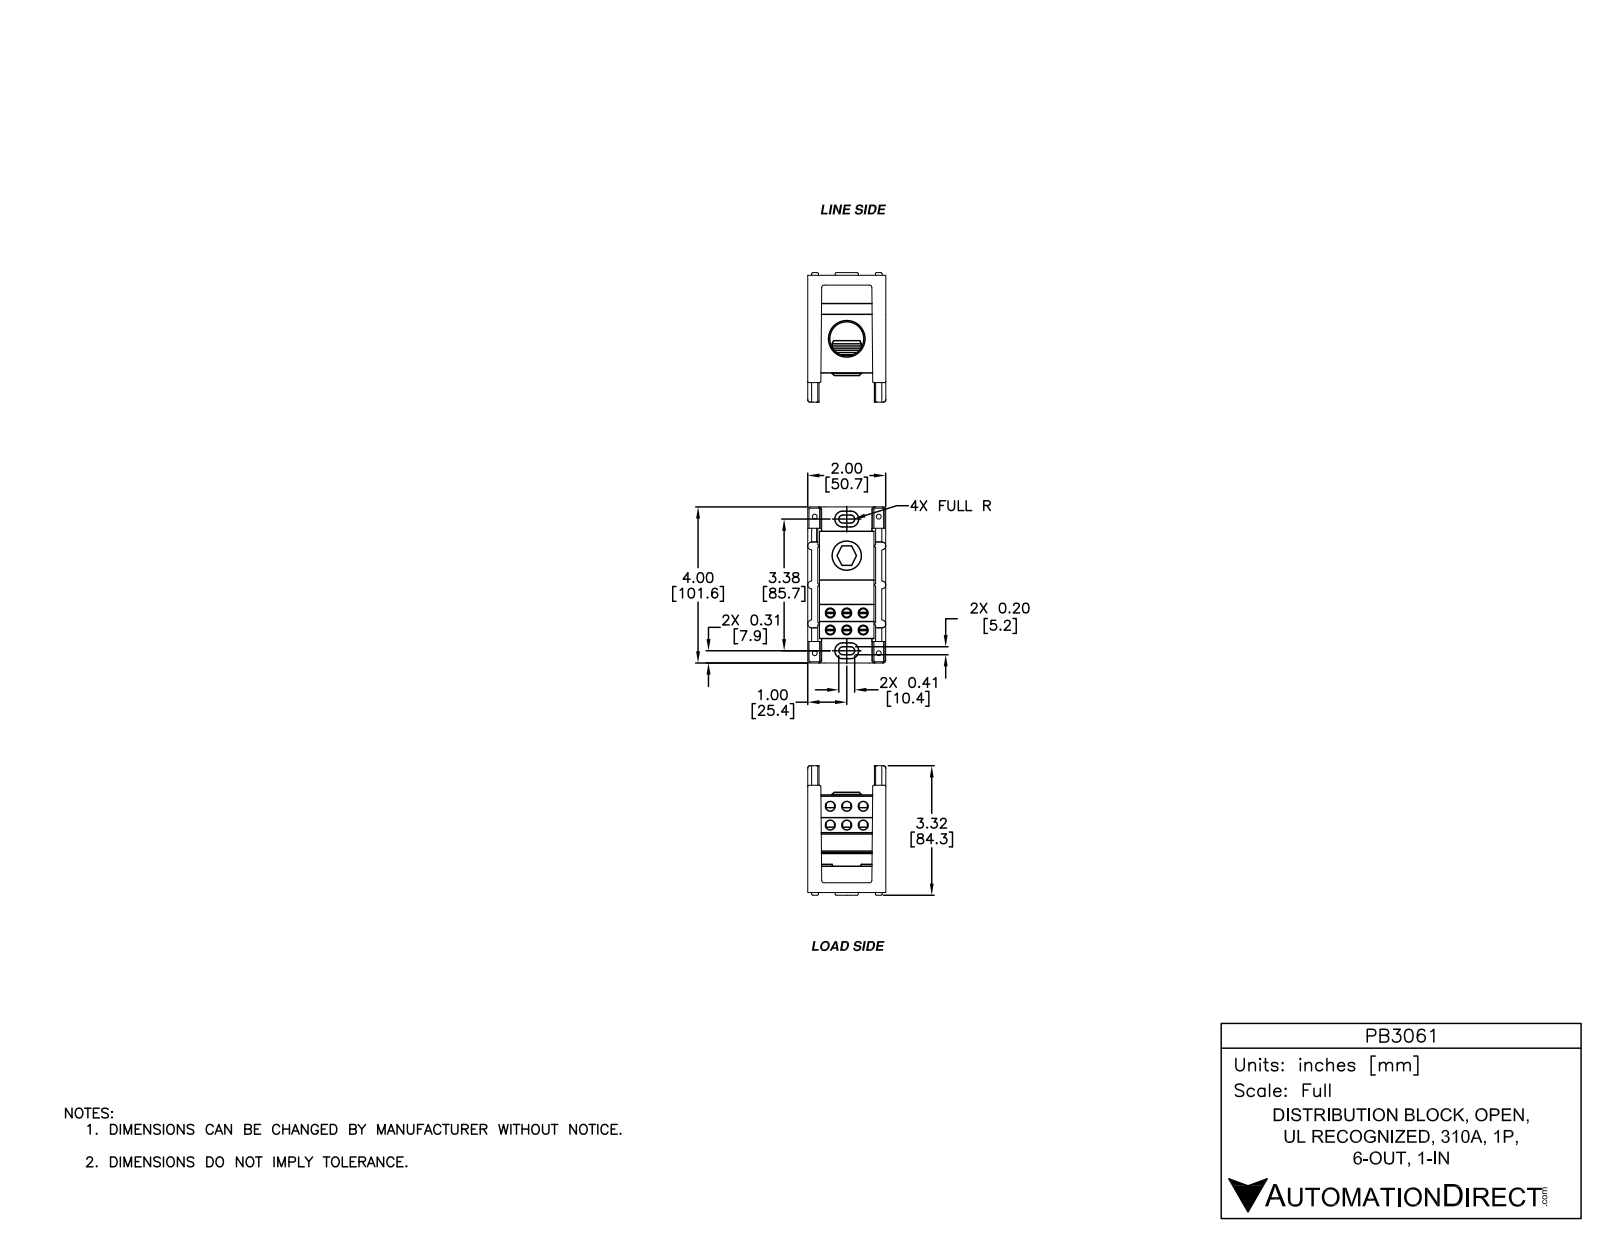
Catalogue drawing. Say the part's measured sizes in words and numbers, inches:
The part is named "PB3061". Its 3-D file was written by "SolidWorks 2014 (AUTOMOTIVE_DESIGN)". It is 5 solids with 562 faces: 220 planar, 234 cylindrical and 108 other. Overall it measures 4 by 3.35 by 2 inches. Its volume is 11.09 cubic inches and its surface area 117.4 square inches. Round holes: 6 of diameter 0.219, 6 of diameter 0.25, 4 of diameter 0.125, 2 of diameter 0.75, 1 of diameter 0.5, 1 of diameter 0.875. Round bosses or shafts: 4 of diameter 0.174, 2 of diameter 0.062, 1 of diameter 0.375. Partial cylindrical surfaces (rounded edges, fillets, slot ends): 50 of radius 0.031, 22 of radius 0.1, 18 of radius 0.063, 12 of radius 0.062, 8 of radius 0.203, 4 of radius 0.094. The main face-to-face distances are 1.641, 0.1, 0.159, 0.259, 1.9, 1.741, 0.301, 1.699, 0.201, 1.599. The hole center spacings are 0.422, 0.608, 0.641, 0.845, 1.933, 0.437, 0.482, 0.446.
